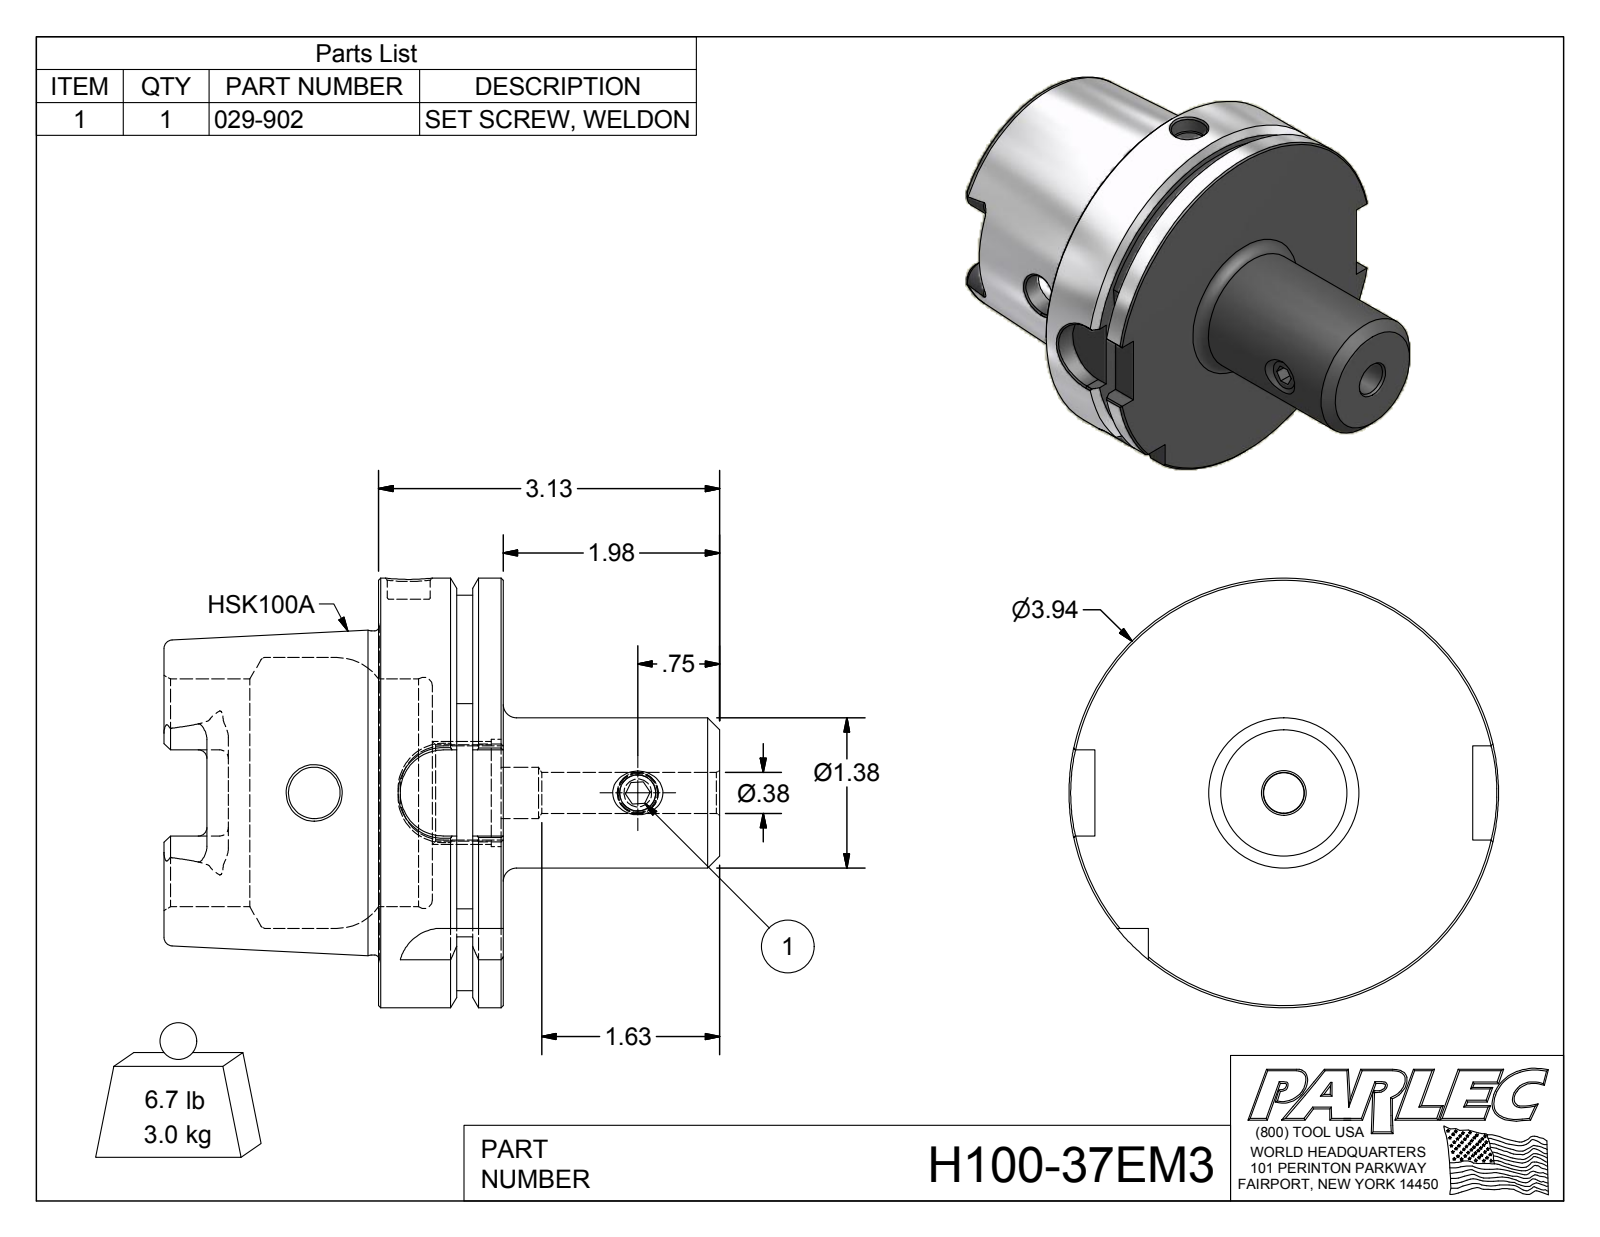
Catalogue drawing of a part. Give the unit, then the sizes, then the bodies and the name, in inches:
Units: inches
Overall size (bounding box): 5.094 × 3.937 × 3.937
Round holes (diameter × count): ⌀0.472 ×2, ⌀0.332 ×1, ⌀0.375 ×1, ⌀0.394 ×1, ⌀0.472 ×1, ⌀0.881 ×1, ⌀0.985 ×1, ⌀2.087 ×1, ⌀2.48 ×1
Round bosses / shafts (diameter × count): ⌀3.937 ×1, ⌀2.967 ×1, ⌀1.378 ×1, ⌀0.375 ×1
Partial cylindrical surfaces — rounded edges, fillets, slot ends (radius × count): R0.079 ×6, R0.192 ×4, R0.394 ×4, R1.811 ×1
Main face-to-face distances: 1.142, 0.492, 0.65, 1.969, 2.461, 3.11, 5.093, 3.125, 2.633, 1.983
Hole centre spacings: 2.965
Volume: 18.17 in³ · Surface area: 88.94 in²
Bodies: 2 solids, 144 faces (53 planar, 38 cylindrical, 53 other)
Part name (STEP PRODUCT): H100-37EM3; H100-37EM3-1; 029-902
STEP written by: Autodesk Inventor 2012 (AUTOMOTIVE_DESIGN)
